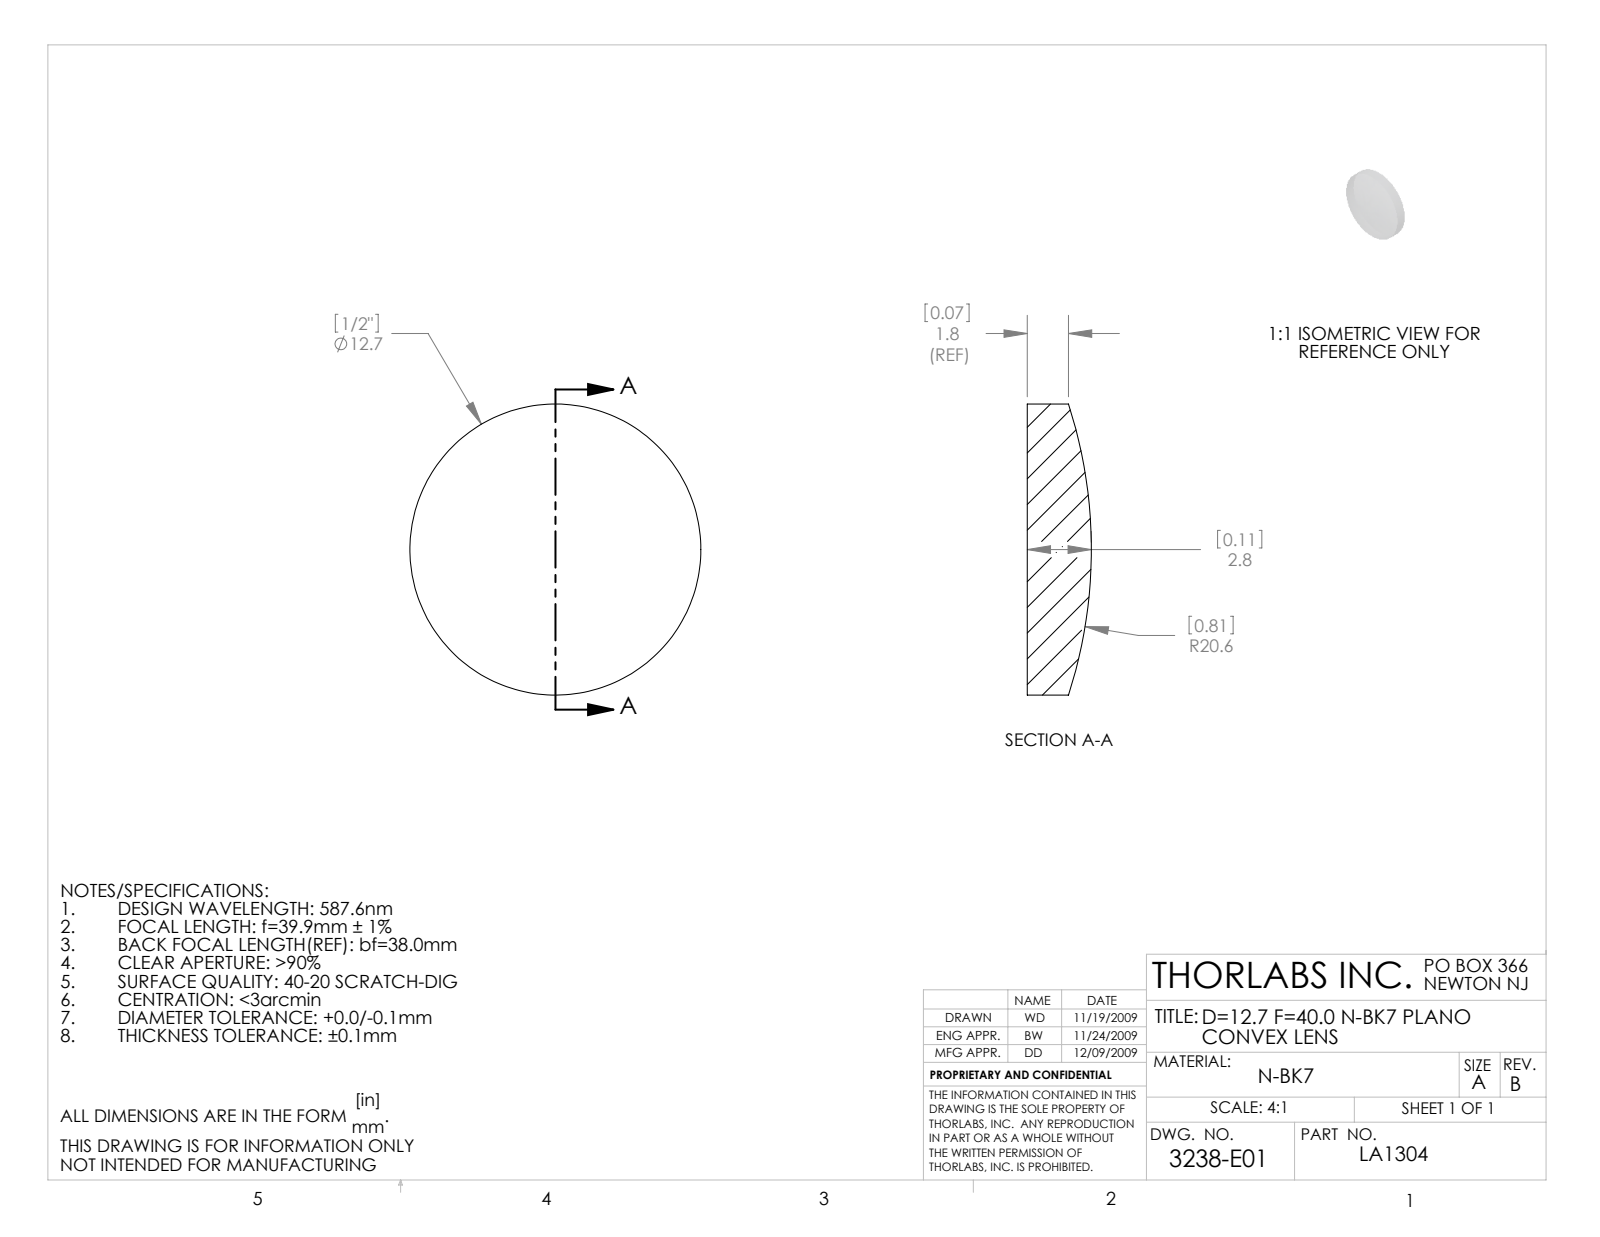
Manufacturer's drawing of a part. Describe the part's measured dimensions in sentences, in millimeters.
The part is named "3238-E0W". Its 3-D file was written by "SolidWorks 2009 (AUTOMOTIVE_DESIGN)". It is 1 solid with 5 faces: 1 planar, 2 cylindrical and 2 other. Overall it measures 12.7 by 12.7 by 2.8 millimeters. Its volume is 292 cubic millimeters and its surface area 328 square millimeters. Round bosses or shafts: 1 of diameter 12.7.
